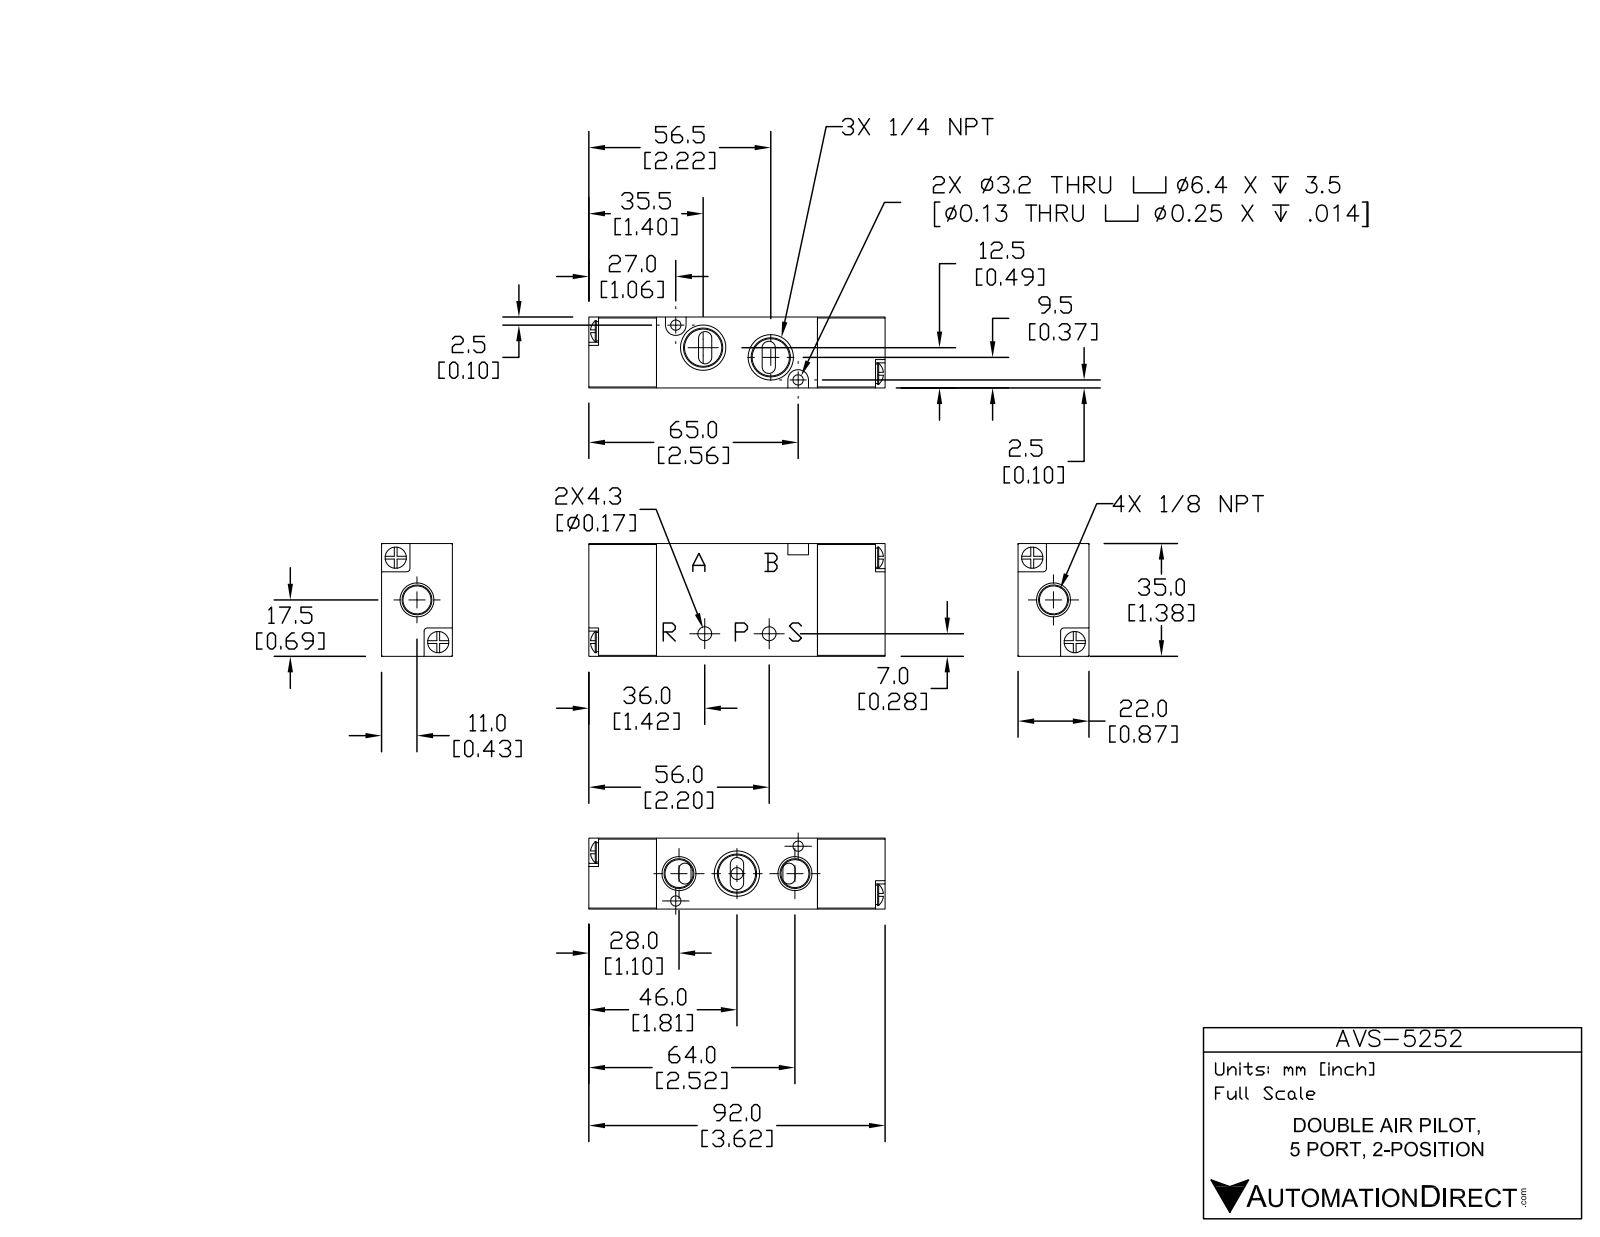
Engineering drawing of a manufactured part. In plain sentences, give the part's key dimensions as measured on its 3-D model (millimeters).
The part is named "AVS-5252". Its 3-D file was written by "SolidWorks 2015 (CONFIG_CONTROL_DESIGN)". It is 3 solids with 199 faces: 99 planar, 56 cylindrical and 44 other. Overall it measures 92 by 35 by 22 millimeters. Its volume is 62 070 cubic millimeters and its surface area 19 060 square millimeters. Round holes: 2 of diameter 3.2, 2 of diameter 4.3, 1 of diameter 3.7. Round bosses or shafts: 4 of diameter 6.6, 4 of diameter 6. Partial cylindrical surfaces (rounded edges, fillets, slot ends): 6 of radius 2.1, 4 of radius 0.3, 4 of radius 1, 4 of radius 1.9, 2 of radius 3.2. The main face-to-face distances are 22, 35, 50, 21, 71, 92, 10.4, 24.6, 14, 3. The hole center spacings are 20.8, 20, 41.6.
